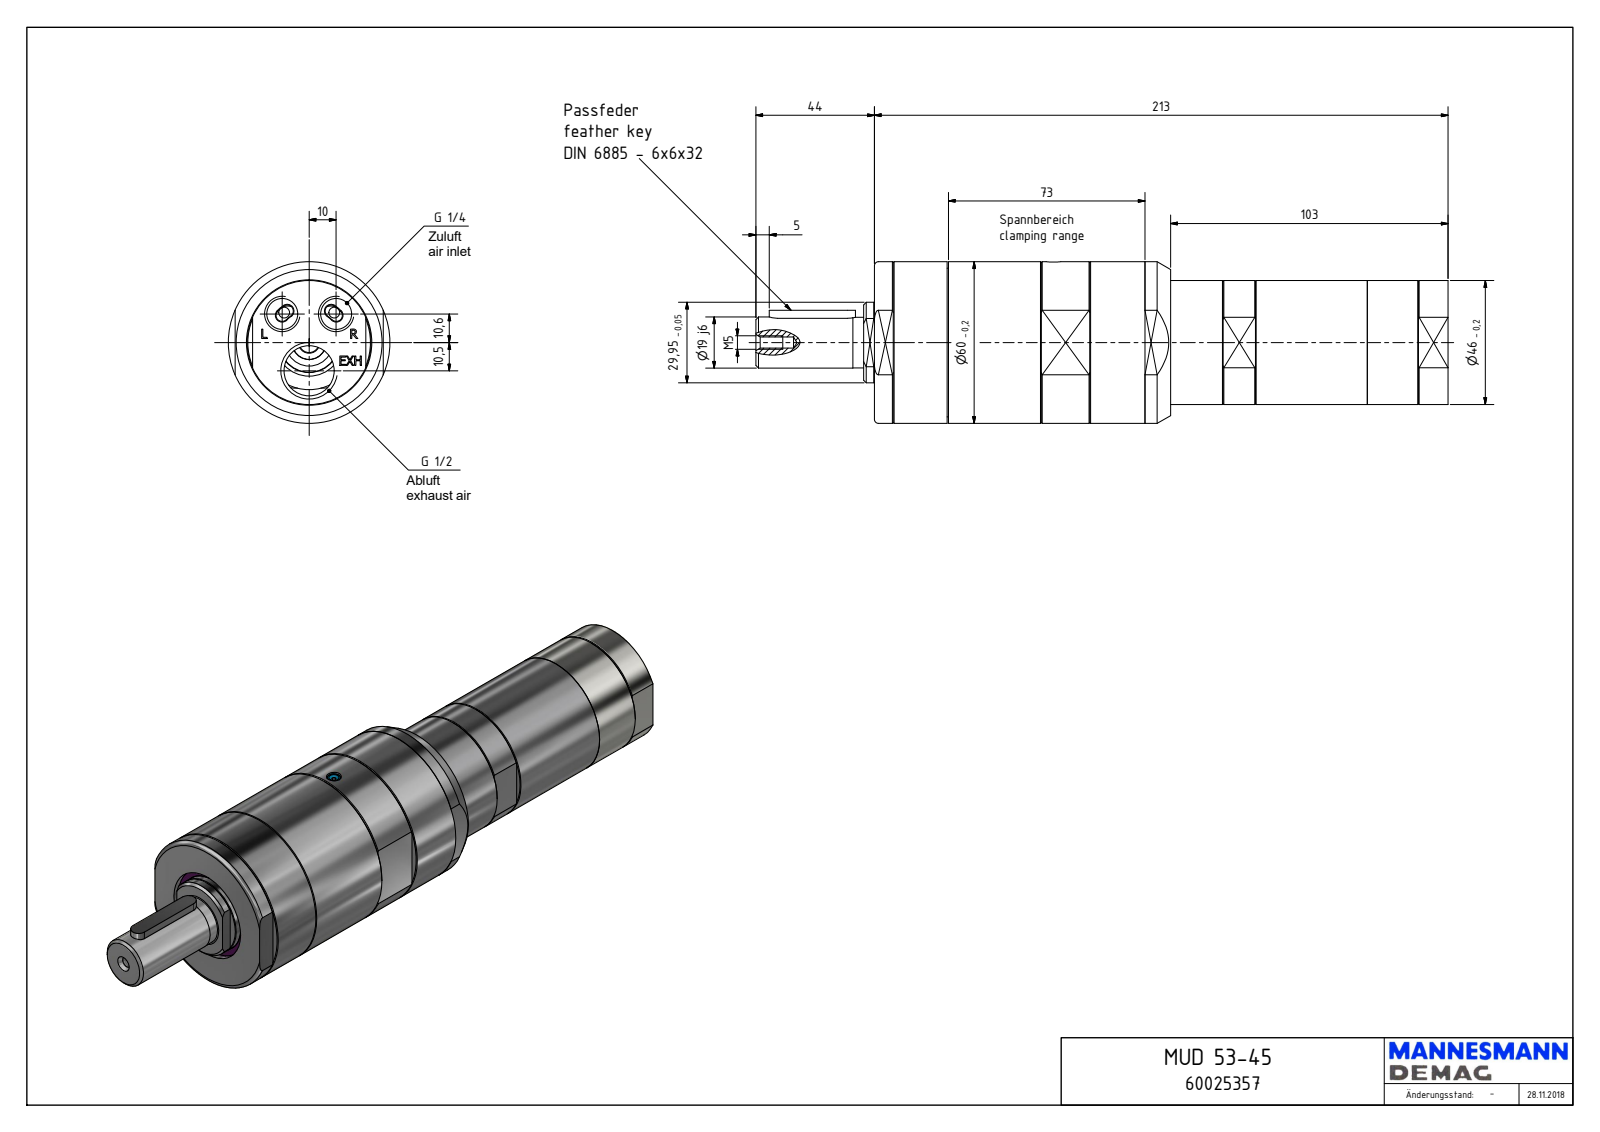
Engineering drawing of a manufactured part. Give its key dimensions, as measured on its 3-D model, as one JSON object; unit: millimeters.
{"part_name": "MUD 53-45_60025357", "step_written_by": "Autodesk Inventor 2018 (AUTOMOTIVE_DESIGN)", "units": "millimeters", "bodies": {"solids": 1, "faces": 212, "planar": 116, "cylindrical": 47, "other": 49}, "overall_size": [257, 60, 60], "volume_mm3": 485108, "surface_area_mm2": 51524, "round_holes": [[11.45, 2], [1.55, 1], [4, 1], [4.13, 1], [5.5, 1], [18.63, 1], [35, 1], [40, 1], [46.5, 1], [55.38, 1]], "round_bosses_or_shafts": [[60, 1], [55.18, 1], [46, 1], [29.95, 1], [19, 1], [18.8, 1], [5, 1], [3.6, 1]], "partial_cylinders_radius": [[3, 2], [5, 2], [17.28, 1], [19, 1], [26.45, 1]], "face_to_face_distances": [6.5, 103, 110, 213, 48.5, 55, 0.5, 76, 107.5, 7], "hole_center_spacings": [14.57, 23.35, 10.5, 20]}
